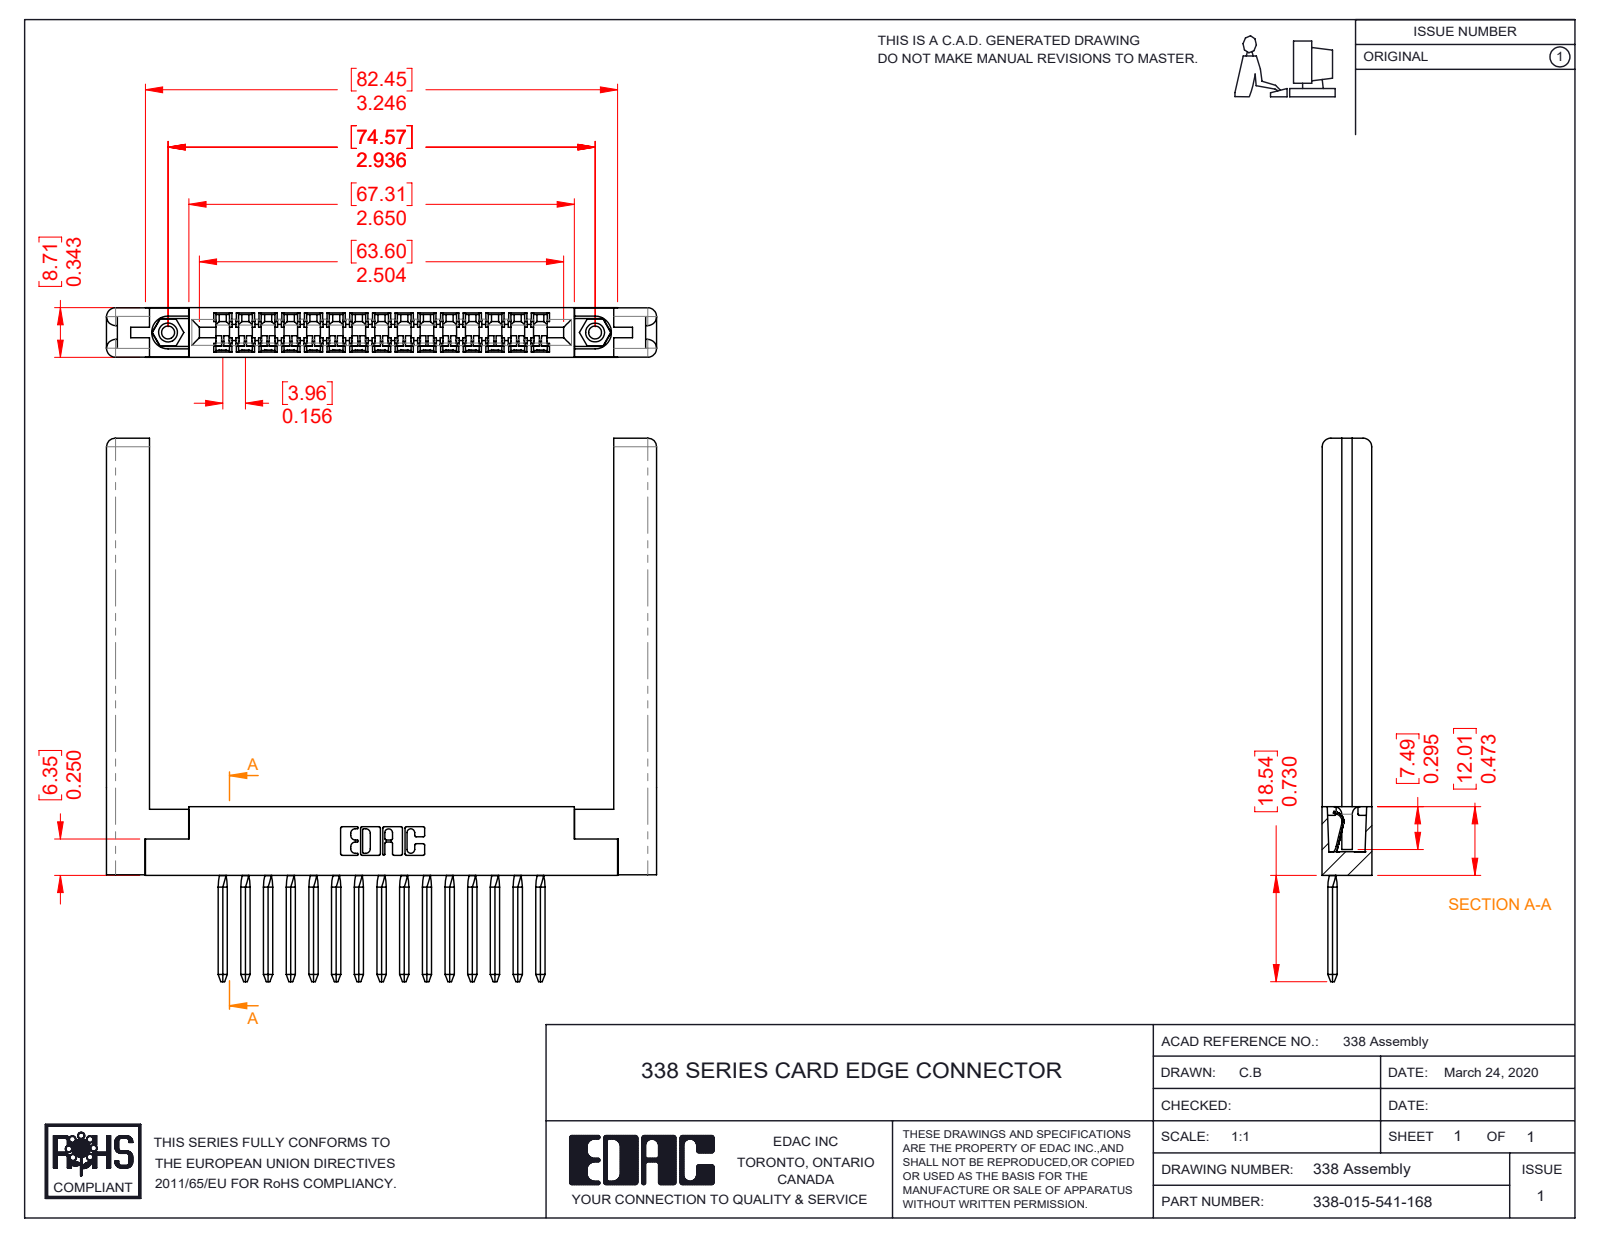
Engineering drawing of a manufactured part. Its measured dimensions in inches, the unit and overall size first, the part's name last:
Units: inches
Overall size (bounding box): 3.782 × 3.735 × 0.343
Round holes (diameter × count): ⌀0.089 ×2, ⌀0.125 ×2, ⌀0.156 ×2
Round bosses / shafts (diameter × count): ⌀0.155 ×2
Partial cylindrical surfaces — rounded edges, fillets, slot ends (radius × count): R0.025 ×62, R0.01 ×22, R0.008 ×15, R0.055 ×12, R0.067 ×12, R0.1 ×12, R0.061 ×8, R0.007 ×6
Main face-to-face distances: 0.341, 0.34, 0.136, 0.343, 0.207, 0.134, 0.206, 3.192, 0.22, 0.071
Hole centre spacings: 2.936
Volume: 0.874 in³ · Surface area: 24.2 in²
Bodies: 20 solids, 1631 faces (1109 planar, 438 cylindrical, 84 other)
Part name (STEP PRODUCT): 338-015-541-168; 307-220-058; 345-250-001_345-250-001-102; 338-290-001_541 (+1 more)
STEP written by: SolidWorks 2016 (CONFIG_CONTROL_DESIGN)
